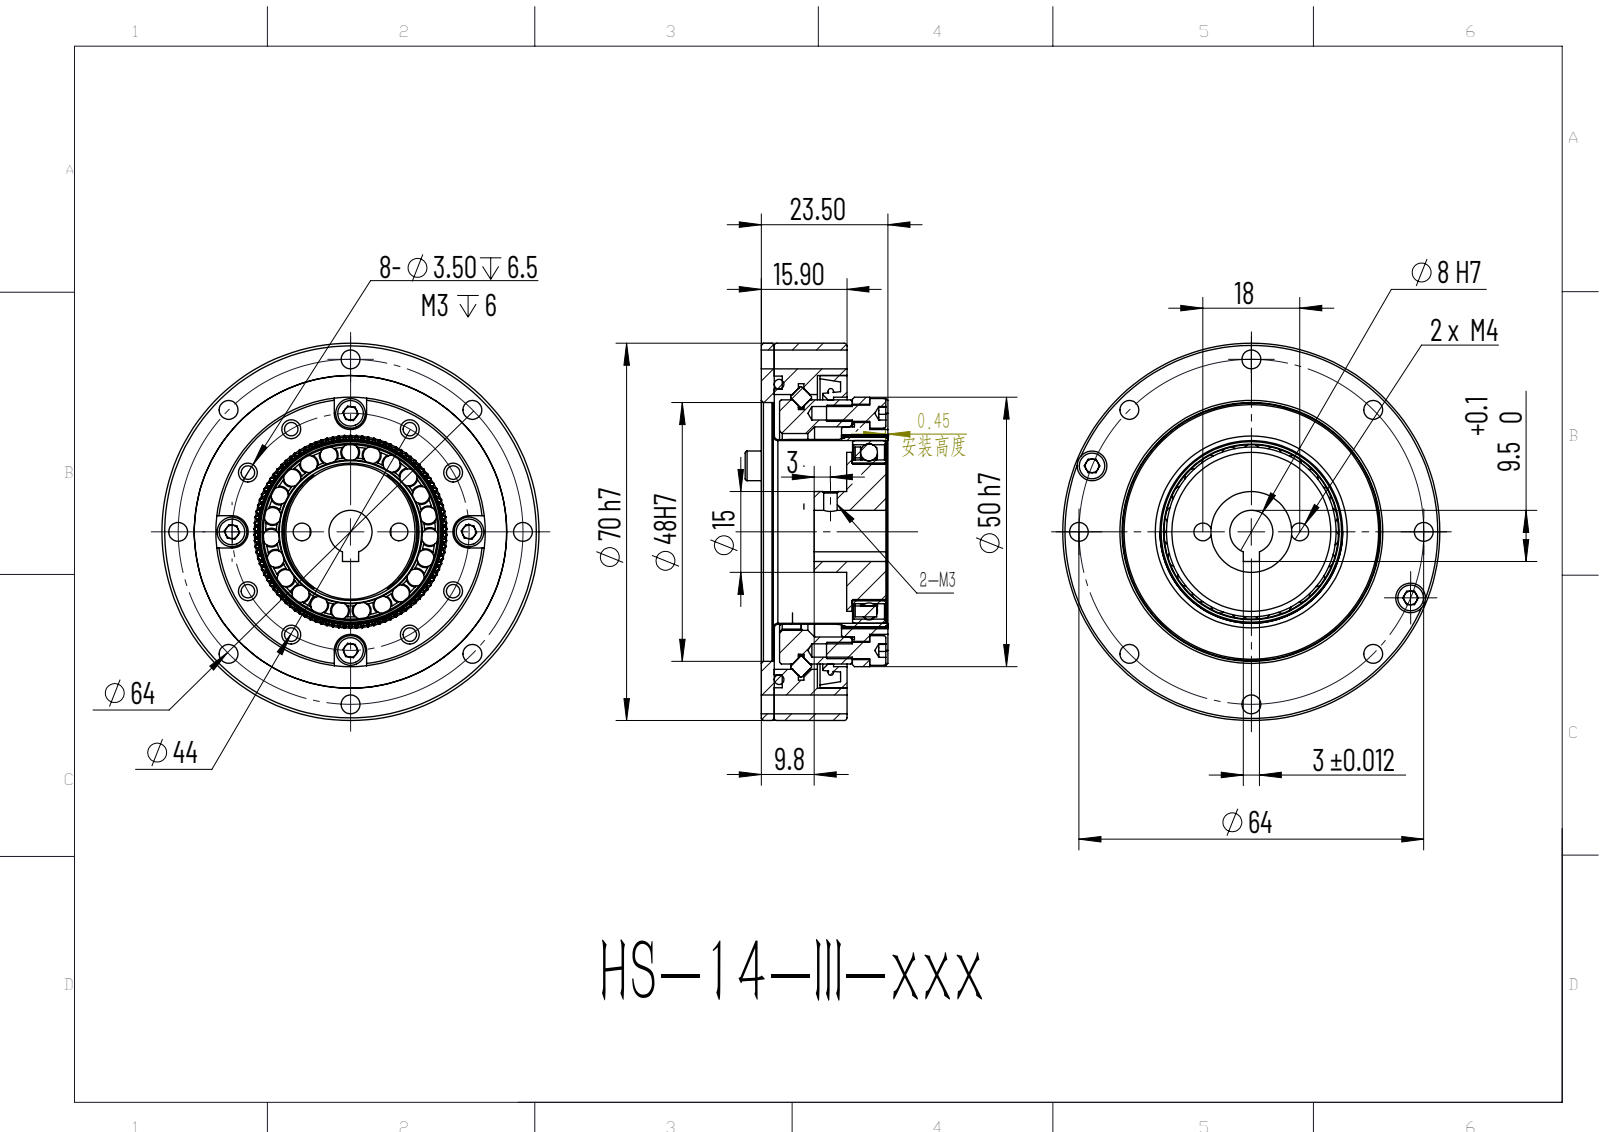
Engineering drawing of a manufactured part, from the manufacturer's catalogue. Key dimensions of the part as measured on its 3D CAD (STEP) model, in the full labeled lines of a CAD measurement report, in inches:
Part name (STEP PRODUCT): HS-14-III; hexagon socket head cap screws gb_GB_FASTENER_SCREWS_HSHCS M3X8-C; 14-50??????_?? <1>; 14???? (+8 more)
STEP written by: ONSHAPE BY PTC INC, 1.201 (AP242_MANAGED_MODEL_BASED_3D_ENGINEERING_MIM_LF)
Units: inches
Bodies: 96 solids, 817 faces (408 planar, 232 cylindrical, 177 other)
Overall size (bounding box): 2.756 × 2.756 × 1.043
Volume: 2.998 in³ · Surface area: 74.17 in²
Round holes (diameter × count): ⌀0.138 ×18, ⌀0.098 ×16, ⌀0.134 ×4, ⌀0.13 ×2, ⌀0.063 ×1, ⌀0.094 ×1, ⌀0.165 ×1, ⌀0.315 ×1, ⌀0.987 ×1, ⌀1.274 ×1, ⌀1.335 ×1, ⌀1.381 ×1
Round bosses / shafts (diameter × count): ⌀0.118 ×46, ⌀0.217 ×6, ⌀2.756 ×1, ⌀2.087 ×1, ⌀1.929 ×1, ⌀1.787 ×1, ⌀1.46 ×1, ⌀1.386 ×1
Partial cylindrical surfaces — rounded edges, fillets, slot ends (radius × count): R0.06 ×40, R0.118 ×4
Main face-to-face distances: 0.039, 0.531, 0.094, 0.626, 0.665, 0.571, 0.256, 0.315, 0.276, 0.492
Hole centre spacings: 0.866, 1.225, 1.5, 1.673, 1.26, 0.448, 0.479, 0.669
